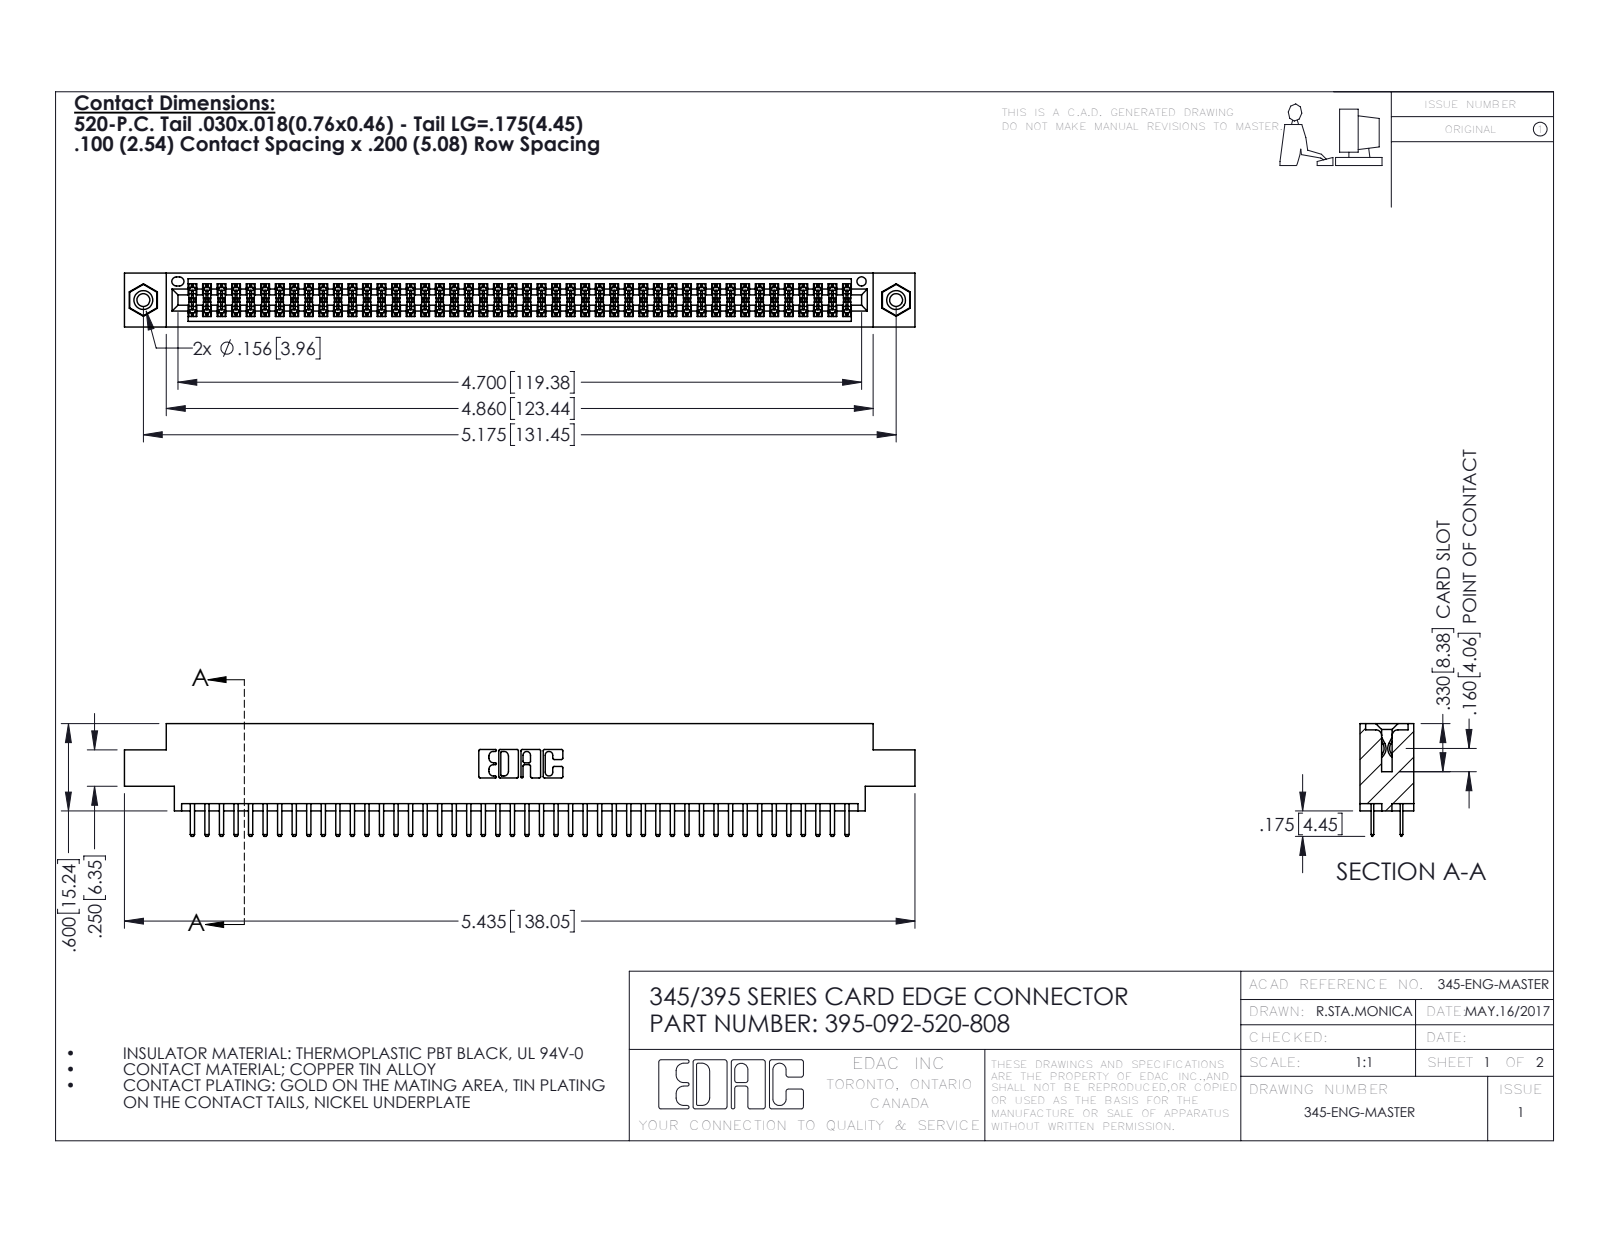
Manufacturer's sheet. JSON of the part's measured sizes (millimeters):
{"part_name": "395-092-520-808; 345 Part_0.170 Offset - 0.156 Dia-TI; 345-292-001_345-293-120; 345-250-001_345-250-003-102", "step_written_by": "SolidWorks 2016 (CONFIG_CONTROL_DESIGN)", "units": "millimeters", "bodies": {"solids": 95, "faces": 5158, "planar": 3336, "cylindrical": 1806, "other": 16}, "overall_size": [138, 19.7, 9.4], "volume_mm3": 13300, "surface_area_mm2": 19790, "round_holes": [[2.3, 2], [3.2, 2], [4, 2], [1.6, 1]], "round_bosses_or_shafts": [[3.9, 2]], "partial_cylinders_radius": [[0.2, 139], [0.3, 96], [0.3, 22], [0.2, 6], [0.8, 6], [0.7, 3], [0.4, 2], [0.5, 2]], "face_to_face_distances": [1.8, 7.6, 5.1, 9.4, 2.5, 6.9, 0.6, 5.7, 0.6, 1.8], "hole_center_spacings": [6.9, 125.5, 131.4]}
